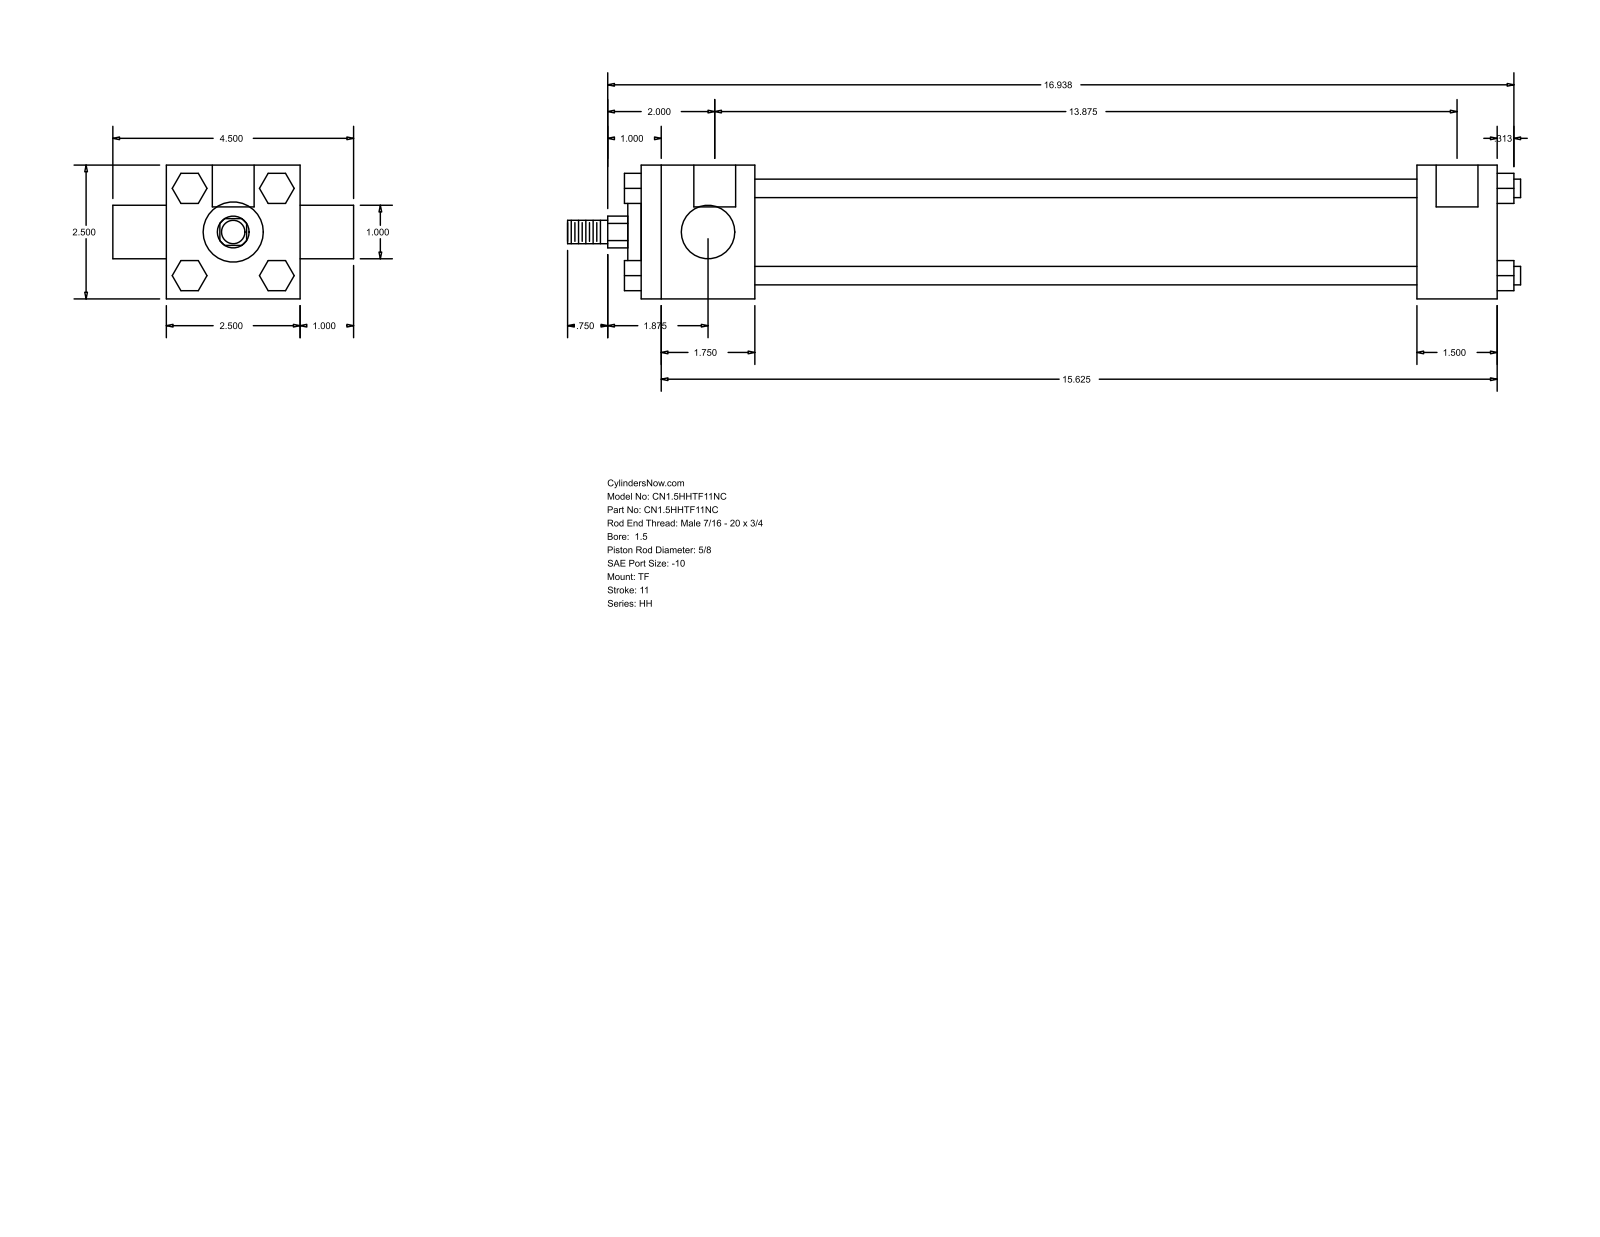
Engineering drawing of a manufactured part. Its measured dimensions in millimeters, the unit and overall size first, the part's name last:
Units: millimetres
Overall size (bounding box): 452.44 × 114.3 × 63.5
Round holes (diameter × count): ⌀5.56 ×3, ⌀19.84 ×2
Round bosses / shafts (diameter × count): ⌀8.76 ×4, ⌀44.45 ×1, ⌀28.57 ×1, ⌀25.4 ×1, ⌀15.88 ×1, ⌀11.11 ×1
Partial cylindrical surfaces — rounded edges, fillets, slot ends (radius × count): R7.54 ×1
Main face-to-face distances: 63.5, 406.39, 53.97, 352.42, 368.3, 314.33, 38.09, 25.4, 88.9, 20.7
Hole centre spacings: 1.58, 1.59, 352.43, 354.01, 354.02, 355.6
Bodies: 0 solids, 120 faces (92 planar, 28 cylindrical, 0 other)
Part name (STEP PRODUCT): HH_TF__0150_0.625
STEP written by: GSSL Pune (CONFIG_CONTROL_DESIGN)
